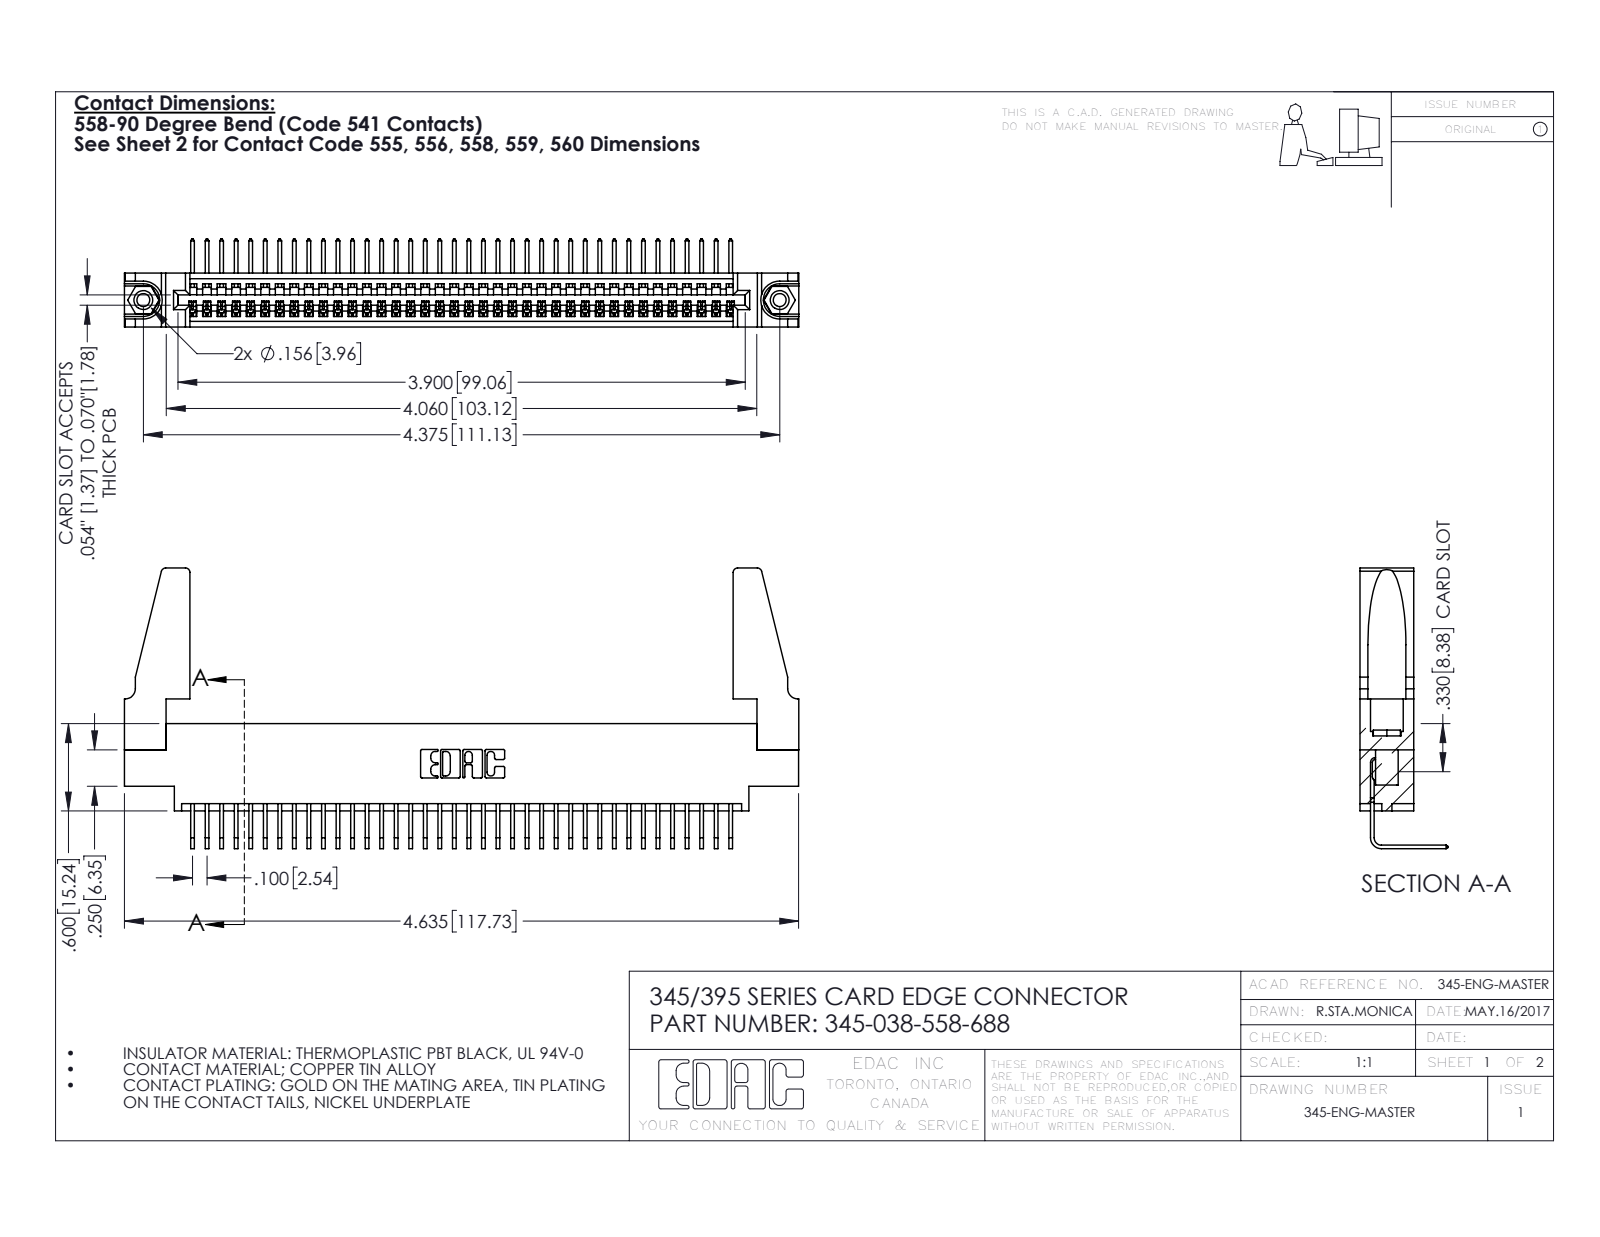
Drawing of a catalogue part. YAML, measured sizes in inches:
part_name: "345-250-001_345-250-001-102; 345-292-001_558 Tail - 2; 345 Part_0.170 Offset - 0.156 Dia-TH; 345-220-078_345-220-088 (+1 more)"
step_written_by: "SolidWorks 2016 (CONFIG_CONTROL_DESIGN)"
units: inches
bodies: {solids: 43, faces: 2534, planar: 1752, cylindrical: 766, other: 16}
overall_size: [4.636, 1.929, 0.605]
volume: 0.88
surface_area: 29.11
round_holes:
  - {diameter: 0.089, count: 2}
  - {diameter: 0.125, count: 2}
  - {diameter: 0.156, count: 2}
  - {diameter: 0.064, count: 1}
round_bosses_or_shafts:
  - {diameter: 0.155, count: 2}
partial_cylinders:
  - {radius: 0.006, count: 76}
  - {radius: 0.01, count: 22}
  - {radius: 0.03, count: 8}
  - {radius: 0.007, count: 6}
  - {radius: 0.031, count: 6}
  - {radius: 0.026, count: 3}
  - {radius: 0.031, count: 2}
  - {radius: 0.04, count: 2}
face_to_face_distances: [0.072, 0.37, 0.298, 0.2, 0.098, 0.272, 0.025, 0.225, 0.175, 0.149]
hole_center_spacings: [0.27, 4.139, 4.375]
